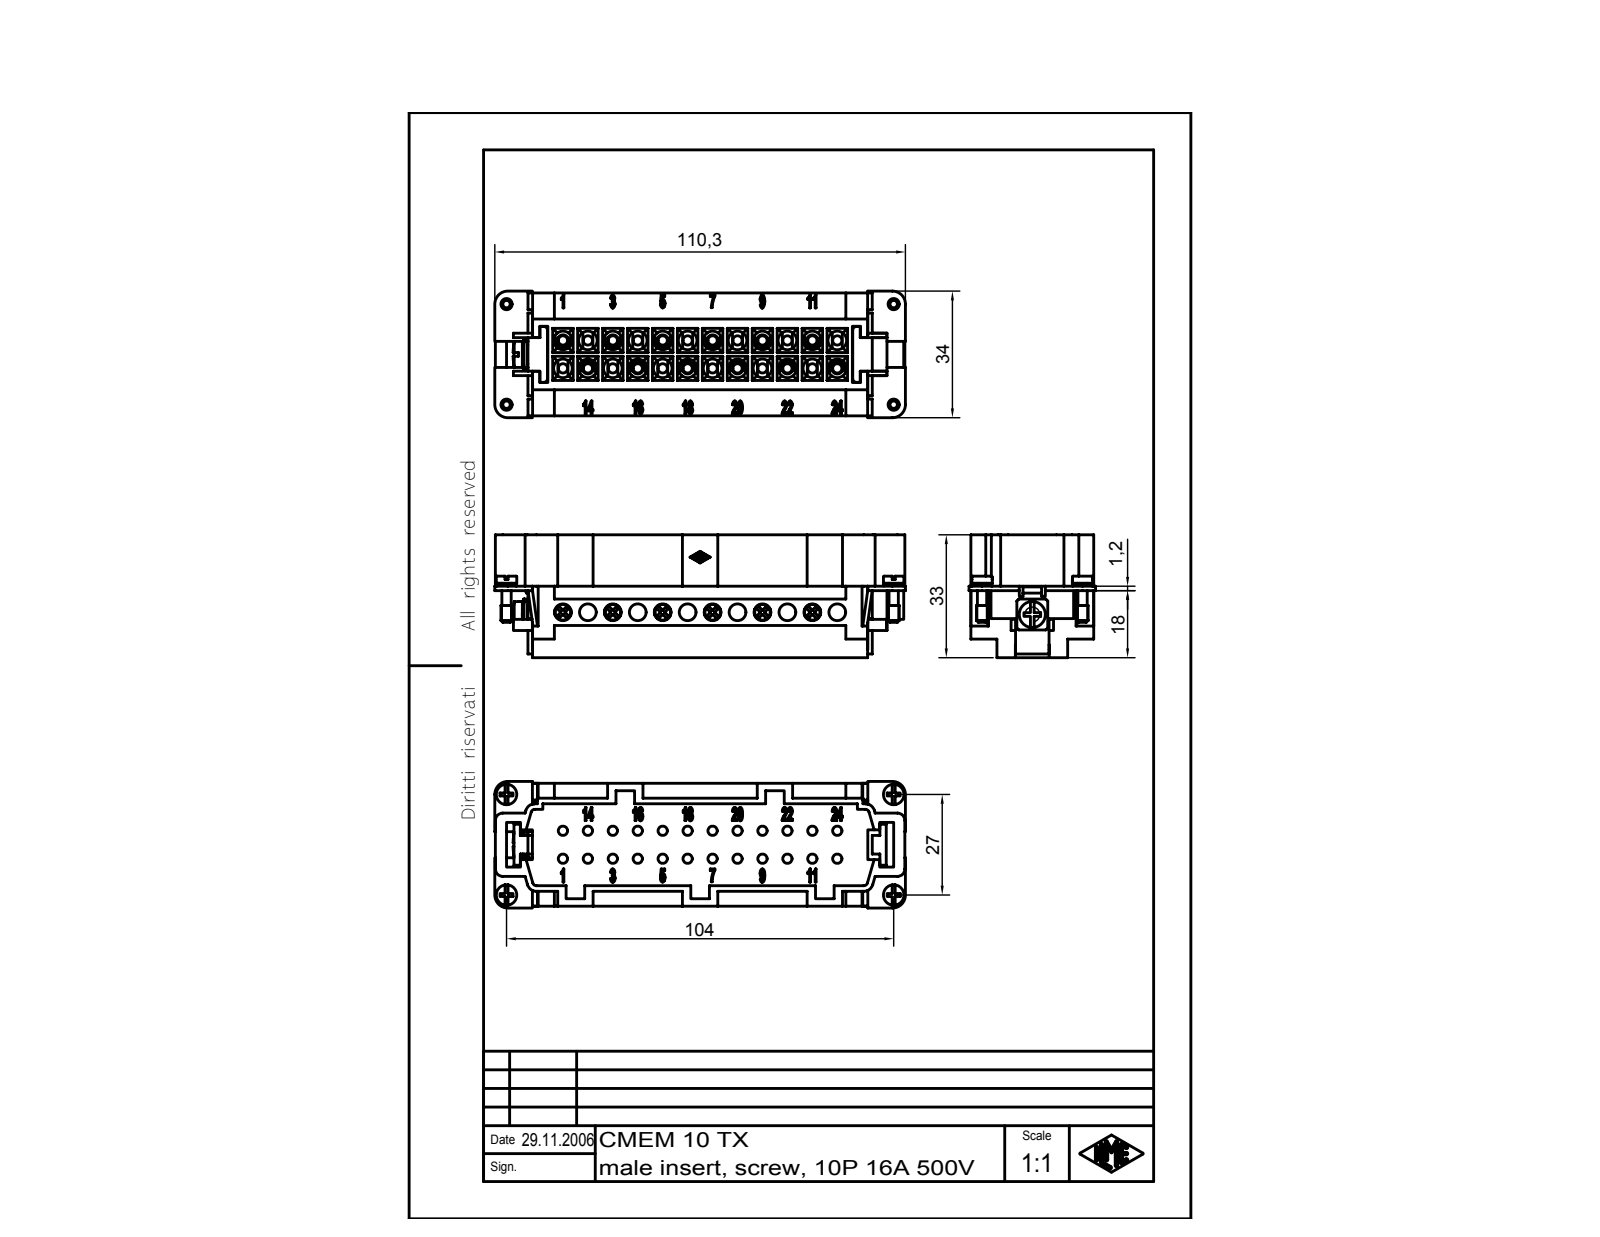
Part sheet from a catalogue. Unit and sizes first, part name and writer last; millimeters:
Units: millimetres
Overall size (bounding box): 110.3 × 34 × 33
Round holes (diameter × count): ⌀2.5 ×12, ⌀3 ×12, ⌀4.5 ×12, ⌀5 ×12, ⌀2.55 ×2
Round bosses / shafts (diameter × count): ⌀4.2 ×12, ⌀2.5 ×8, ⌀5.5 ×2, ⌀5.3 ×2, ⌀3 ×2, ⌀7 ×1
Partial cylindrical surfaces — rounded edges, fillets, slot ends (radius × count): R0.1 ×14, R2.1 ×12, R1 ×6, R2 ×6, R2.5 ×4, R3.5 ×2, R1.62 ×1, R5.5 ×1
Main face-to-face distances: 1.5, 22, 3, 20.5, 4, 7, 5.5, 29, 23.5, 26
Hole centre spacings: 6.7, 13.4, 20.1, 26.8, 10.06, 33.5, 15.36, 21.45
Volume: 44 016 mm³ · Surface area: 39 951 mm²
Bodies: 13 solids, 2429 faces (1162 planar, 311 cylindrical, 956 other)
Part name (STEP PRODUCT): CMEM 10 TX
STEP written by: Autodesk Inventor 7 (AUTOMOTIVE_DESIGN)
